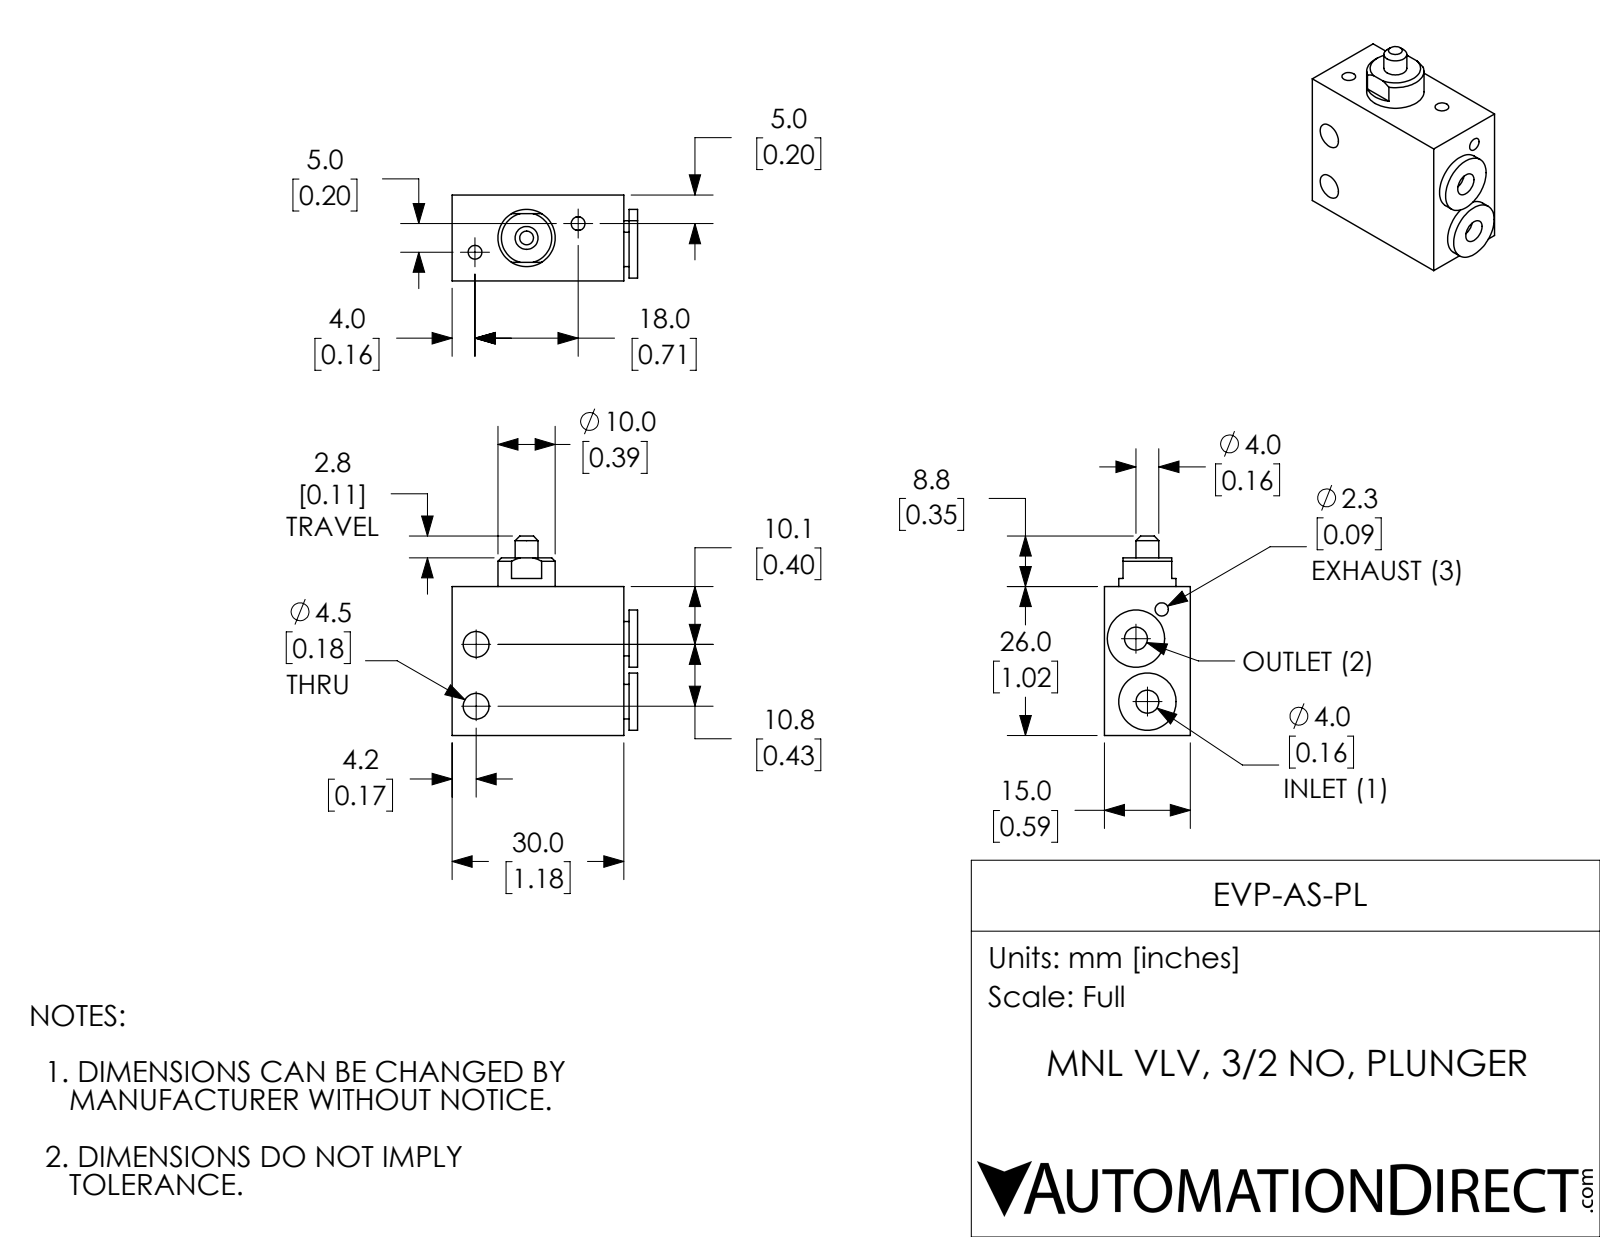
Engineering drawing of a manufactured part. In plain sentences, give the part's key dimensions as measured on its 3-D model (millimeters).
The part is named "EVP-AS-PL". Its 3-D file was written by "SolidWorks 2017 (AUTOMOTIVE_DESIGN)". It is 1 solid with 53 faces: 22 planar, 27 cylindrical and 4 other. Overall it measures 34.8 by 32.4 by 15 millimeters. Its volume is 11 800 cubic millimeters and its surface area 4 295 square millimeters. Round holes: 2 of diameter 2.4, 2 of diameter 4, 2 of diameter 4.5, 1 of diameter 2.3. Round bosses or shafts: 3 of diameter 10, 2 of diameter 6, 1 of diameter 4. The main face-to-face distances are 15, 26, 30, 32.4, 2.4, 30.9, 0.9, 1.5, 31, 5. The hole center spacings are 6.8, 10.8, 11.2, 16.3, 18.7.
